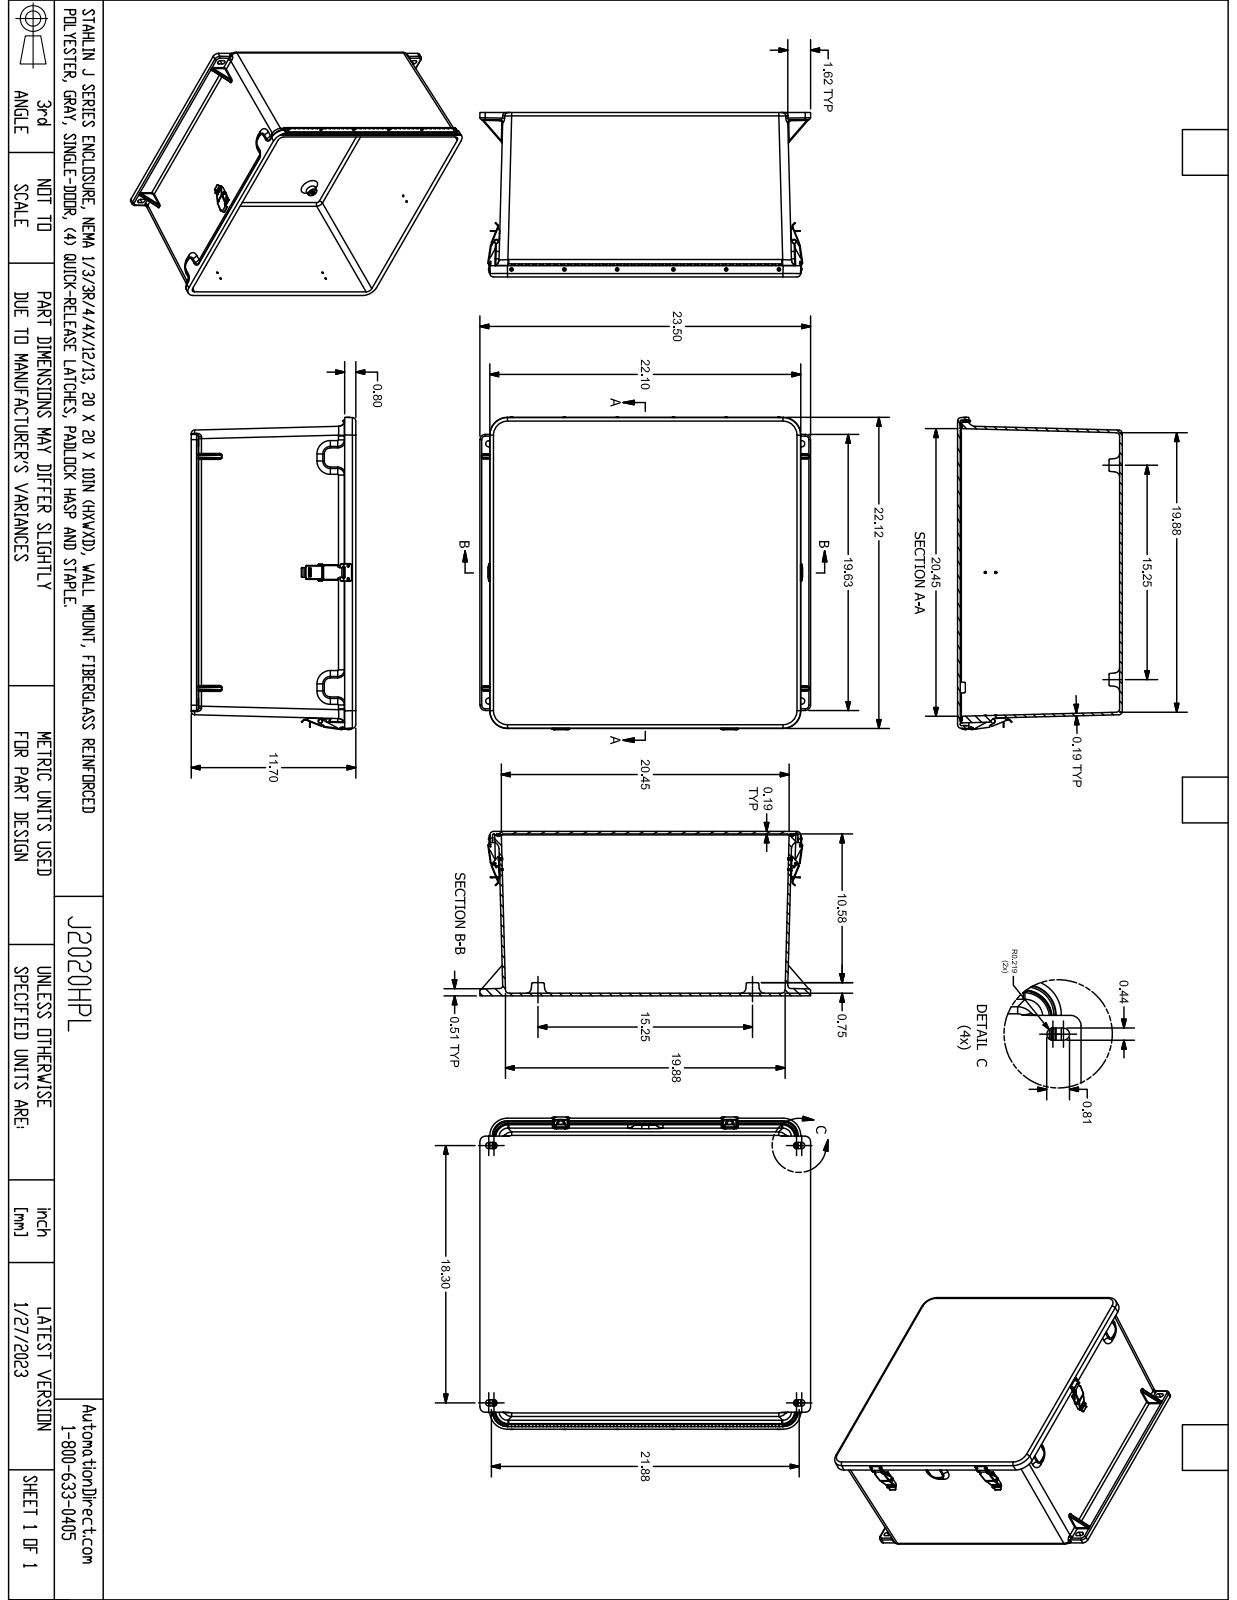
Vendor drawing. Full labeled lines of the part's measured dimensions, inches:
Part name (STEP PRODUCT): M2020HPL
STEP written by: SolidWorks 2018 (AUTOMOTIVE_DESIGN)
Units: inches
Bodies: 62 solids, 2139 faces (803 planar, 878 cylindrical, 458 other)
Overall size (bounding box): 23.5 × 22.223 × 11.701
Volume: 434.8 in³ · Surface area: 4 099 in²
Round holes (diameter × count): ⌀0.104 ×28, ⌀0.139 ×24, ⌀0.131 ×12, ⌀0.13 ×8, ⌀0.14 ×8, ⌀0.135 ×6, ⌀0.204 ×4, ⌀0.313 ×4, ⌀0.375 ×4, ⌀0.135 ×3, ⌀0.31 ×2, ⌀0.085 ×1
Round bosses / shafts (diameter × count): ⌀0.125 ×20, ⌀0.125 ×8, ⌀0.391 ×4, ⌀0.3 ×3, ⌀0.17 ×3, ⌀0.12 ×3, ⌀0.155 ×1, ⌀0.155 ×1
Partial cylindrical surfaces — rounded edges, fillets, slot ends (radius × count): R0.005 ×72, R0.015 ×44, R0.125 ×40, R0.02 ×32, R0.045 ×32, R0.03 ×24, R0.06 ×22, R0.5 ×17
Main face-to-face distances: 0.188, 11.513, 0.188, 11.701, 11.325, 0.286, 0.474, 21.262, 11.438, 11.25
Hole centre spacings: 3.75, 7.5, 0.937, 12, 11, 11.5, 15.25, 7.25
